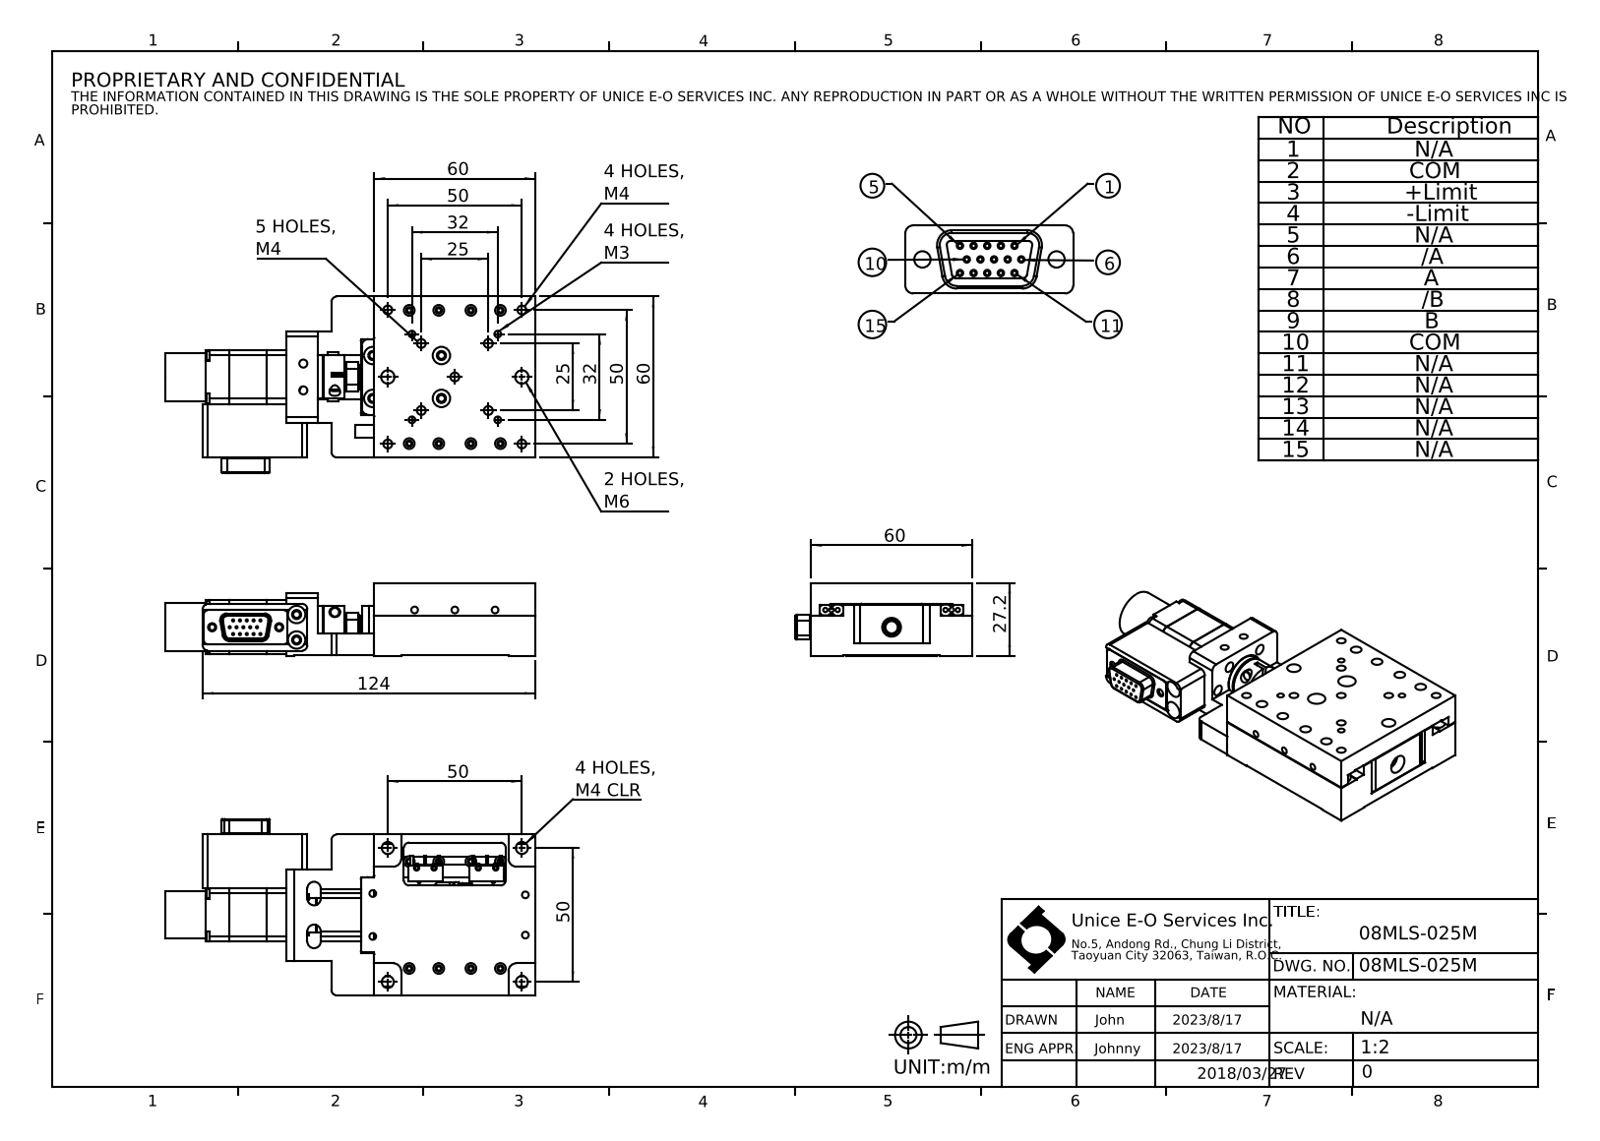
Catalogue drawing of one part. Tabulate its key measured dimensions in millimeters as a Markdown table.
| quantity | value |
| --- | --- |
| part name | 08MLS-025M |
| STEP written by | SolidWorks 2022 (CONFIG_CONTROL_DESIGN) |
| units | millimeters |
| bodies | 0 solids, 439 faces (242 planar, 180 cylindrical, 17 other) |
| overall size | 138 × 65.83 × 27.2 |
| round holes (diameter × count) | 4 × 18, 0.8 × 15, 2.5 × 13, 3.3 × 9, 6.5 × 8, 7.2 × 6, 2 × 4, 4.5 × 4, 3 × 3, 2.26 × 2, 2.6 × 2, 3.05 × 2 |
| round bosses / shafts (diameter × count) | 3.6 × 4, 4 × 2, 17.8 × 1, 16 × 1, 14.8 × 1, 12 × 1, 8 × 1, 6 × 1 |
| partial cylindrical surfaces (radius × count) | 2 × 18, 2.5 × 9, 0.5 × 8, 1 × 4, 1.5 × 4, 3 × 4, 1.8 × 2, 6.25 × 1 |
| main face-to-face distances | 27, 19.2, 7.8, 60, 4, 4.3, 15.85, 44.15, 20, 18.9 |
| hole center spacings | 2.84, 4.58, 5.08, 2.54, 17.68, 39.53, 25, 6.84 |
